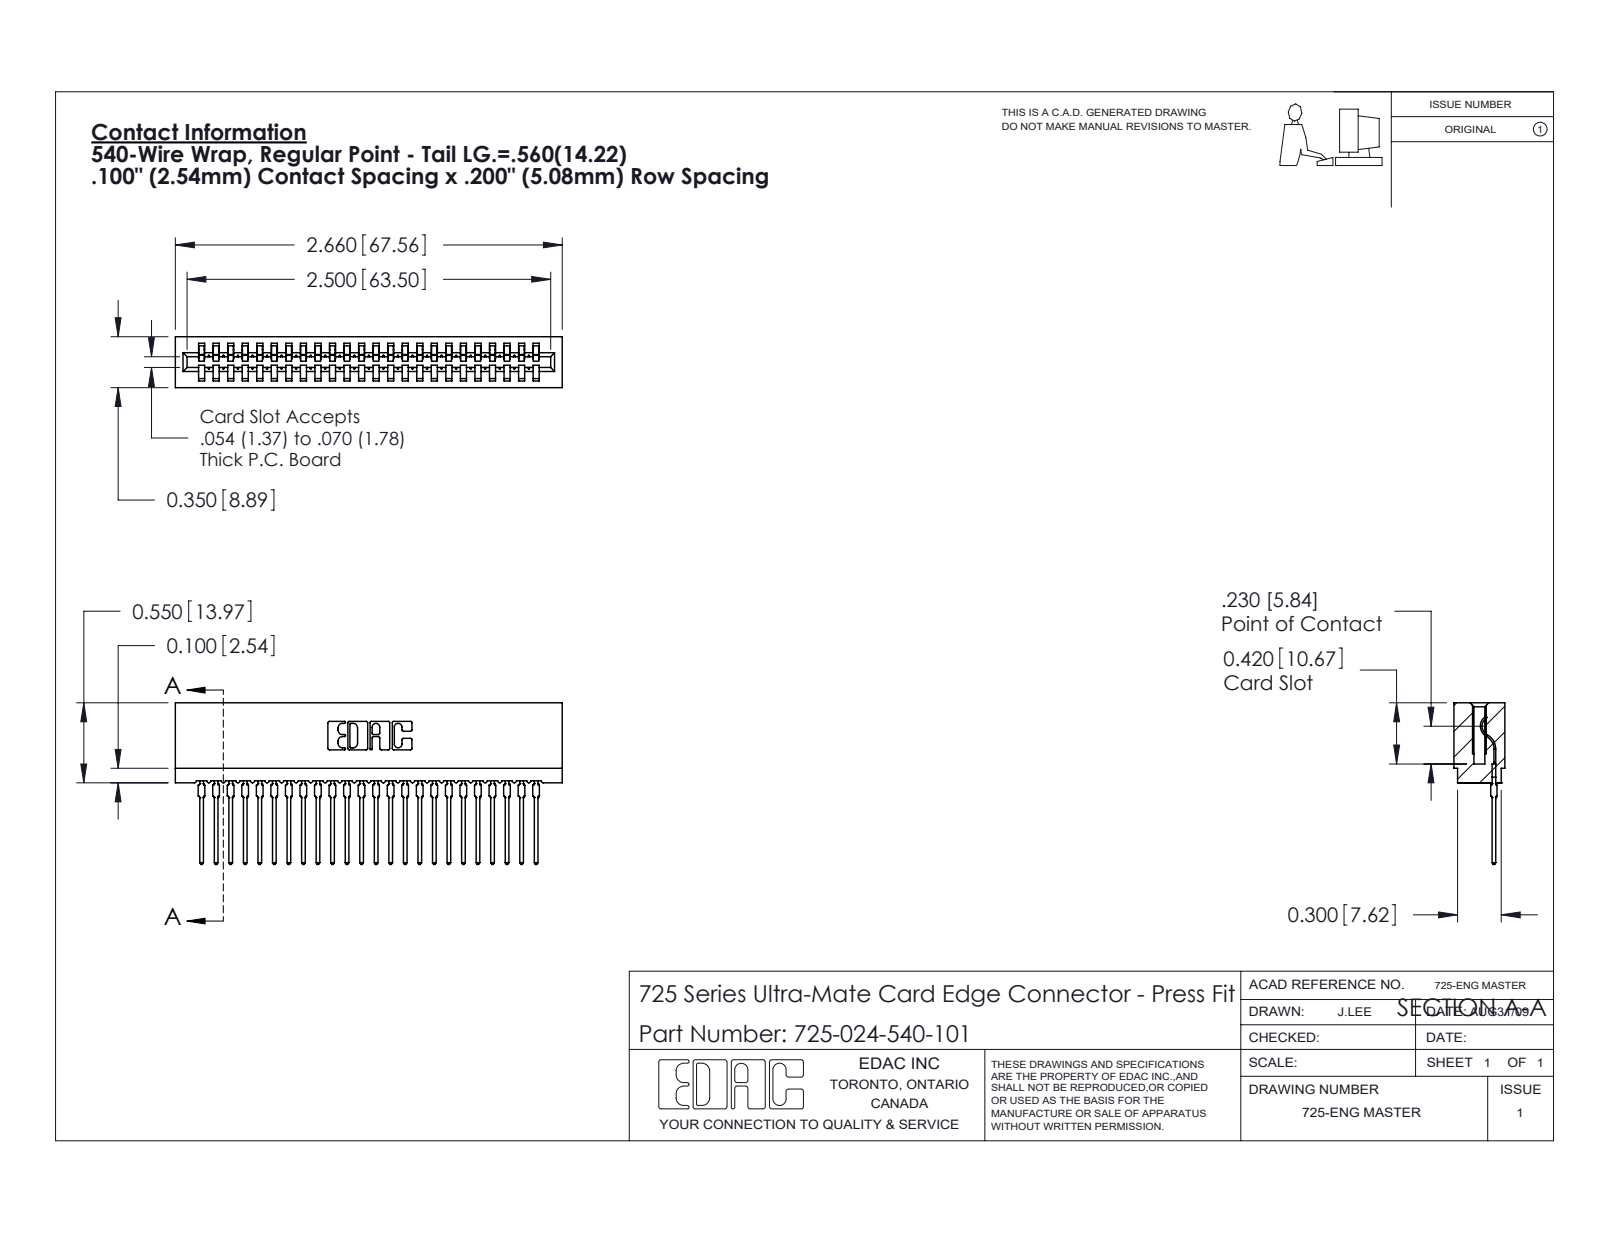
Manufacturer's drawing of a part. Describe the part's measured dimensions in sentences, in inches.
The part is named "725-024-540-101; 725 Part_Insulator Option - 01; 745-292-001_540". Its 3-D file was written by "SolidWorks 2020 (CONFIG_CONTROL_DESIGN)". It is 25 solids with 2783 faces: 1663 planar, 496 cylindrical and 624 other. Overall it measures 2.66 by 1.111 by 0.35 inches. Its volume is 0.322 cubic inches and its surface area 15.67 square inches. Partial cylindrical surfaces (rounded edges, fillets, slot ends): 48 of radius 0.015, 48 of radius 0.021, 22 of radius 0.01, 6 of radius 0.007, 6 of radius 0.031, 4 of radius 0.005, 4 of radius 0.011, 3 of radius 0.026. The main face-to-face distances are 0.2, 0.1, 0.3, 0.4, 0.5, 0.35, 0.6, 0.7, 0.212, 0.138.
